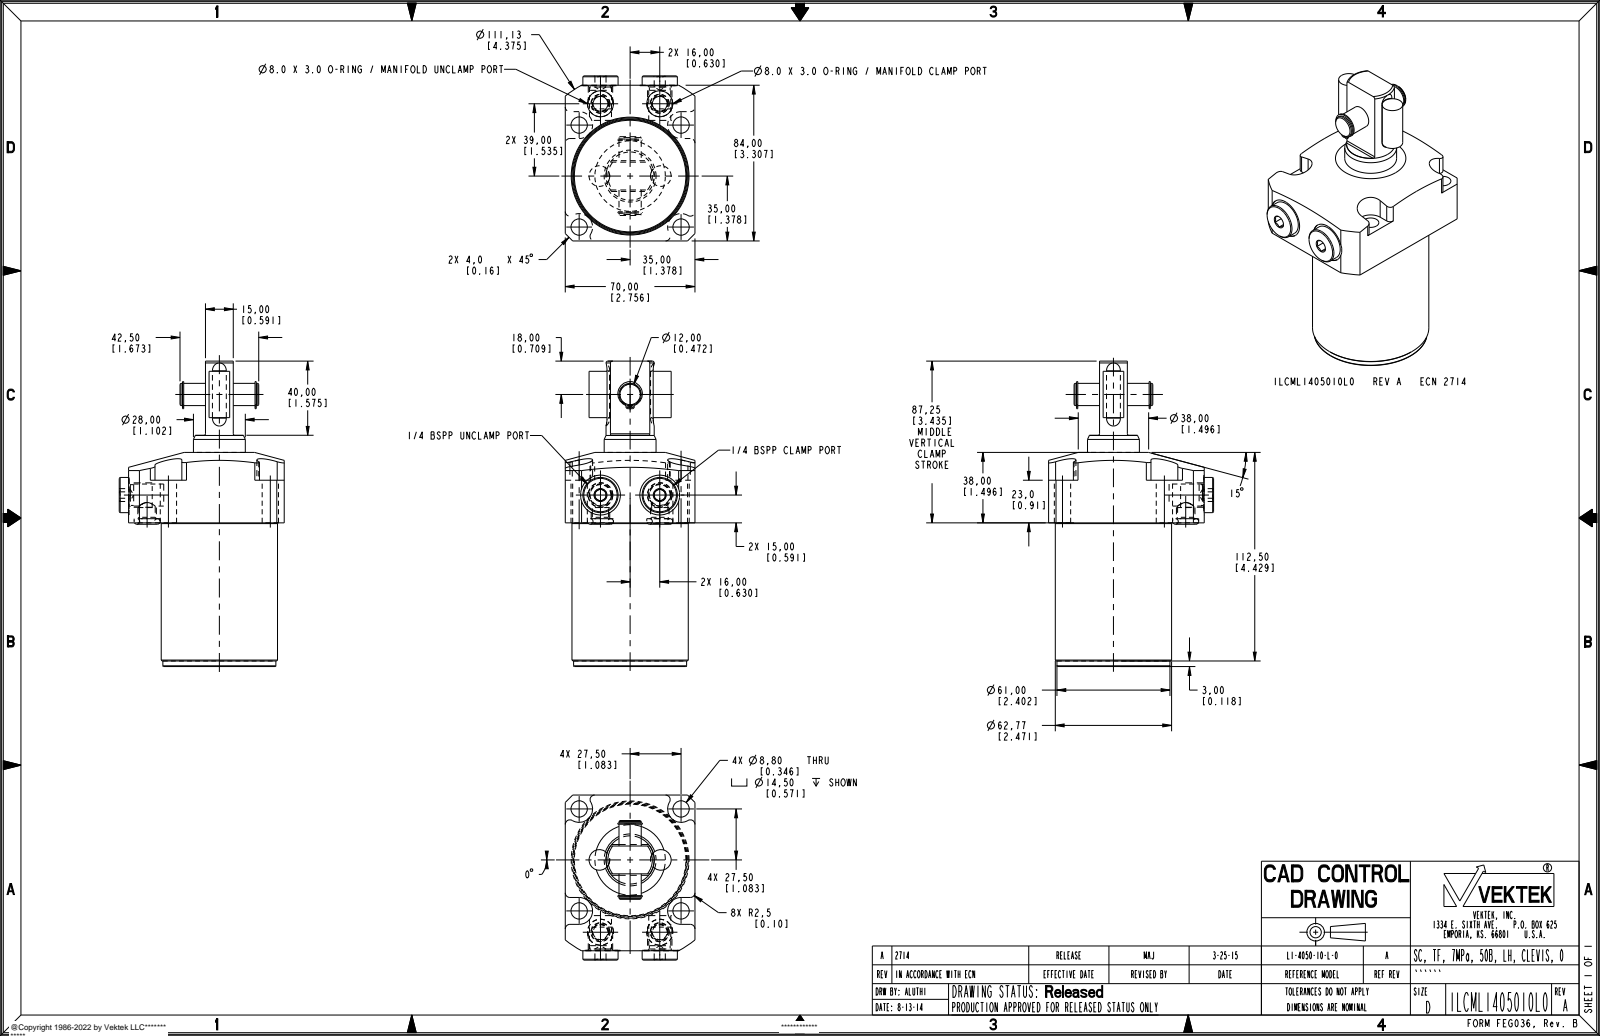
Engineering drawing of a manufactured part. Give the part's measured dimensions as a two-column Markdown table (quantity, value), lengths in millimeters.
| quantity | value |
| --- | --- |
| part name | ILCML1405010L0 |
| STEP written by | PRO/ENGINEER BY PARAMETRIC TECHNOLOGY CORPORATION, 2013320 (AUTOMOTIVE_DESIGN) |
| units | millimeters |
| bodies | 5 solids, 235 faces (85 planar, 102 cylindrical, 48 other) |
| overall size | 164.75 × 89.05 × 70 |
| volume | 453 985 mm³ |
| surface area | 51 384 mm² |
| round holes (diameter × count) | 8.8 × 4, 1.04 × 2, 6 × 2, 8.75 × 2, 11.89 × 2, 14 × 2, 21.5 × 2 |
| round bosses / shafts (diameter × count) | 19 × 2, 13.16 × 2, 11.2 × 2, 11.12 × 2, 10 × 2, 62.77 × 1, 61 × 1, 28 × 1 |
| partial cylindrical surfaces (radius × count) | 2.5 × 8, 7.25 × 4, 0.8 × 2, 1.04 × 2, 1.09 × 2, 5.56 × 2, 55.56 × 1 |
| main face-to-face distances | 70, 77.5, 15, 84, 27.5, 42.5, 41.5, 56.5, 38, 100.5 |
| hole center spacings | 55, 16.26, 32, 44.99, 49.87, 50.63, 67.49, 77.78 |
